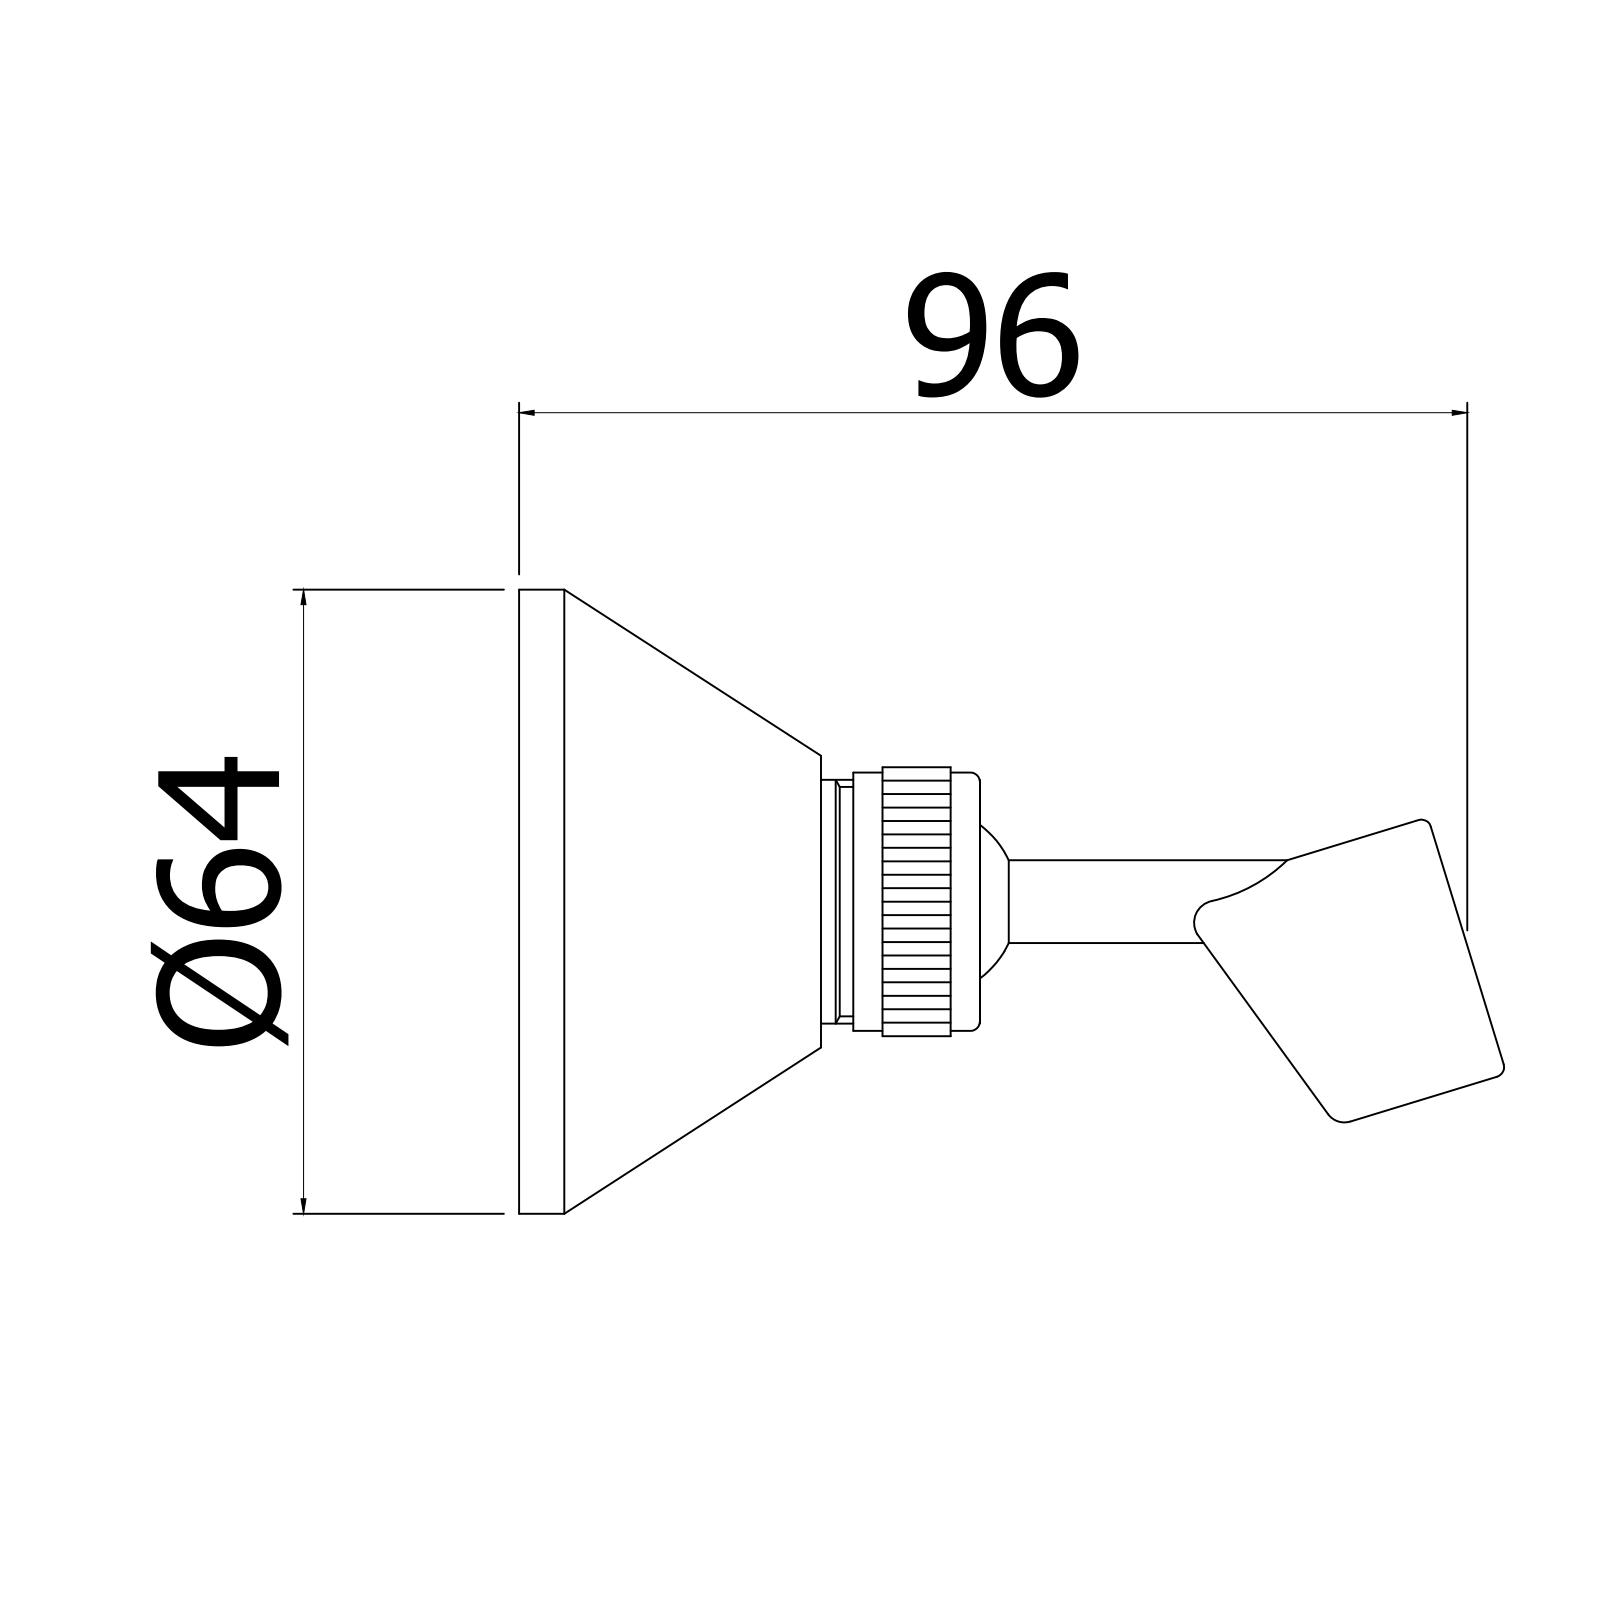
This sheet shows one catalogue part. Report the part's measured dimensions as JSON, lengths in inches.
{"part_name": "ZSUP015CR", "step_written_by": "CREO PARAMETRIC BY PTC INC, 2020044 (CONFIG_CONTROL_DESIGN)", "units": "inches", "bodies": {"solids": 1, "faces": 560, "planar": 186, "cylindrical": 360, "other": 14}, "overall_size": [3.798, 2.603, 2.52], "volume_in3": 1.627, "surface_area_in2": 35.84, "round_holes": [[0.236, 1], [0.669, 1], [0.728, 1], [0.787, 1], [1.079, 1], [2.323, 1]], "round_bosses_or_shafts": [[2.52, 1], [1.161, 1], [0.984, 1], [0.354, 1]], "partial_cylinders_radius": [[0.01, 95], [0.02, 72], [0.502, 1], [0.512, 1], [0.522, 1], [0.618, 1]], "face_to_face_distances": [0.118, 0.846, 0.433, 0.453, 0.571, 0.098, 0.945, 1.673, 0.827, 0.709]}
